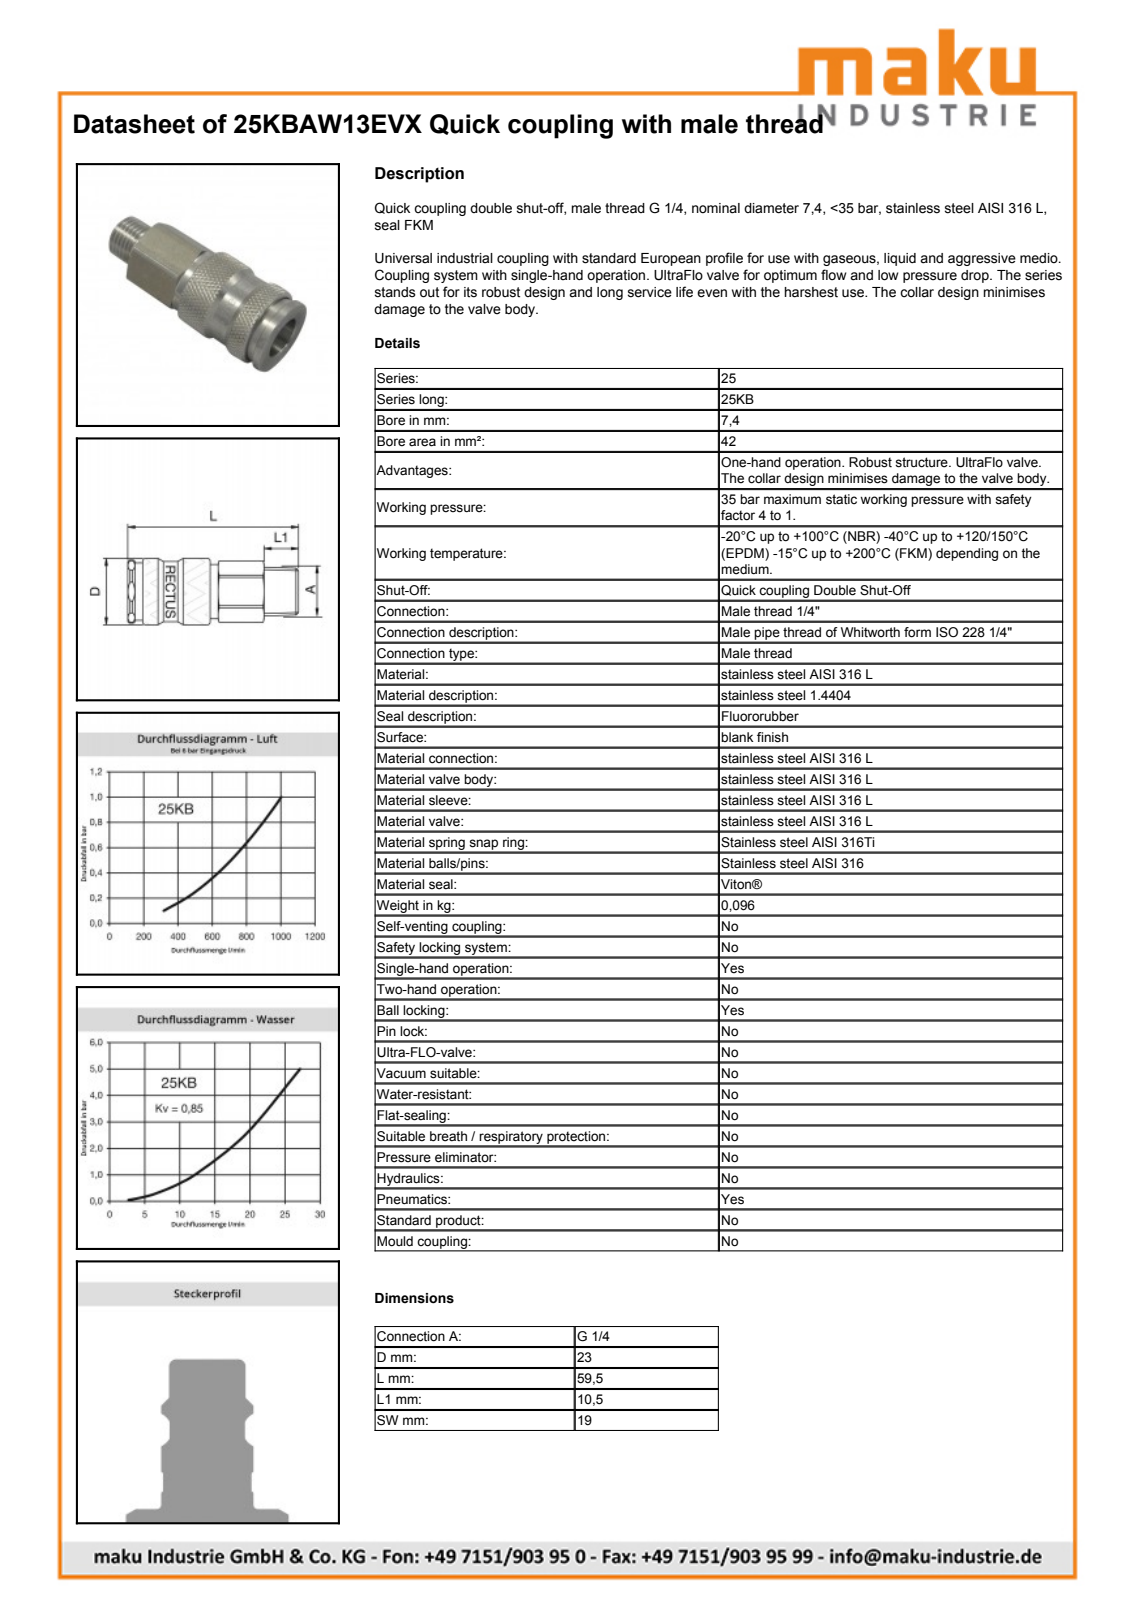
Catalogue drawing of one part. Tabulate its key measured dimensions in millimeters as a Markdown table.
| quantity | value |
| --- | --- |
| part name | D109081 |
| STEP written by | Autodesk Inventor 2013 (AUTOMOTIVE_DESIGN) |
| units | millimeters |
| bodies | 2 solids, 604 faces (239 planar, 82 cylindrical, 283 other) |
| overall size | 59.5 × 23.15 × 23.15 |
| volume | 17 340 mm³ |
| surface area | 8 122 mm² |
| round holes (diameter × count) | 15.1 × 1, 16 × 1, 17.25 × 1, 19.35 × 1, 20.05 × 1 |
| round bosses / shafts (diameter × count) | 23.15 × 1, 22 × 1, 21 × 1, 20 × 1, 18.95 × 1, 17 × 1, 15.3 × 1, 15.05 × 1 |
| partial cylindrical surfaces (radius × count) | 10.4 × 1, 10.7 × 1 |
| main face-to-face distances | 19, 24.5, 59.5, 49, 10.5, 35, 5.25, 19.25, 28.75, 4.25 |
